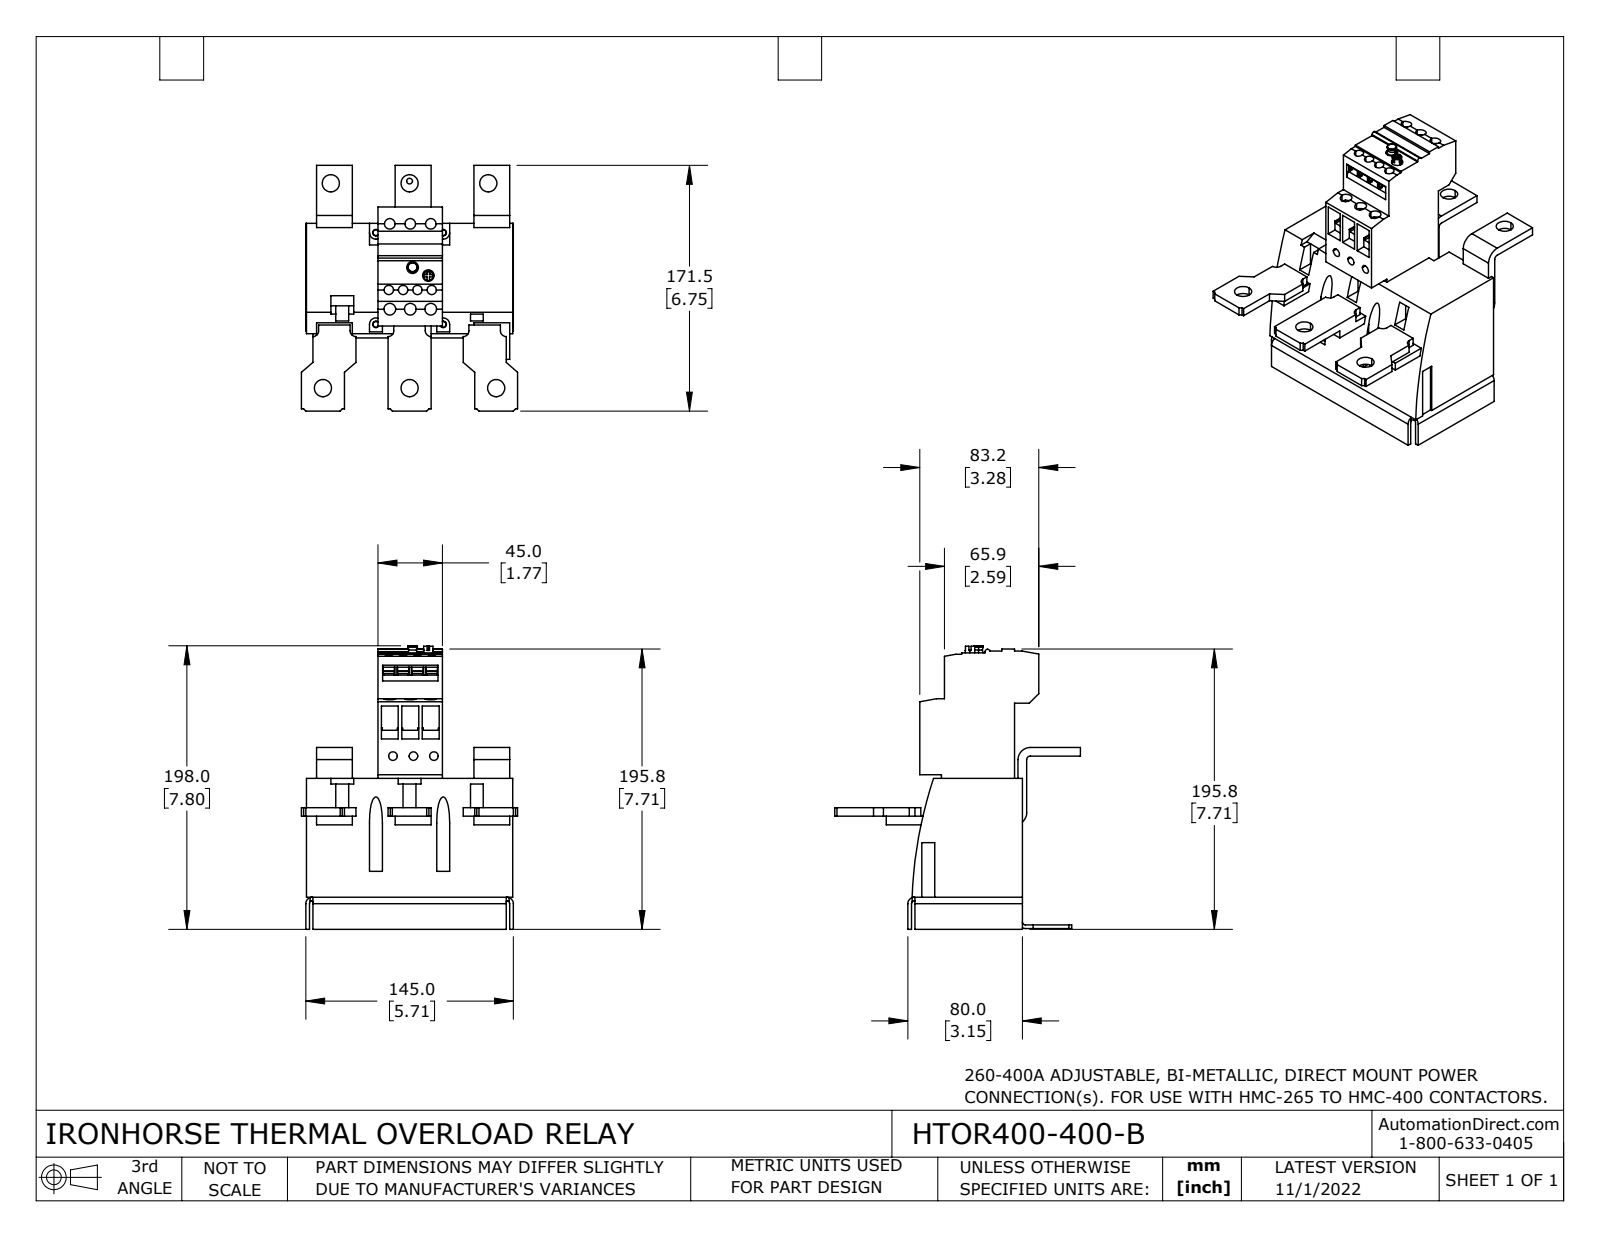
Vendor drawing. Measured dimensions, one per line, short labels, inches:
name: HTOR400-400-B
written by: SolidWorks 2021 (CONFIG_CONTROL_DESIGN)
unit: in
bodies: 7 solids, 528 faces (401 planar, 121 cylindrical, 6 other)
size: 7.795 × 6.752 × 5.945
volume: 71.5 in³; area: 255.9 in²
holes: 6× ⌀0.157, 6× ⌀0.472, 4× ⌀0.177, 4× ⌀0.256, 3× ⌀0.236, 3× ⌀0.291, 3× ⌀0.323, 1× ⌀0.315
bosses: 2× ⌀0.26
rounds: 9× R0.079, 8× R0.157, 5× R0.181, 2× R0.177, 2× R0.177, 2× R0.335, 1× R0.059, 1× R0.069
face distances: 0.102, 3.268, 0.236, 3.37, 1.969, 3.74, 2.461, 1.772, 1.929, 3.701
hole spacings: 0.563, 2.413, 0.394, 1.126, 2.346, 0.528, 0.642, 0.787
